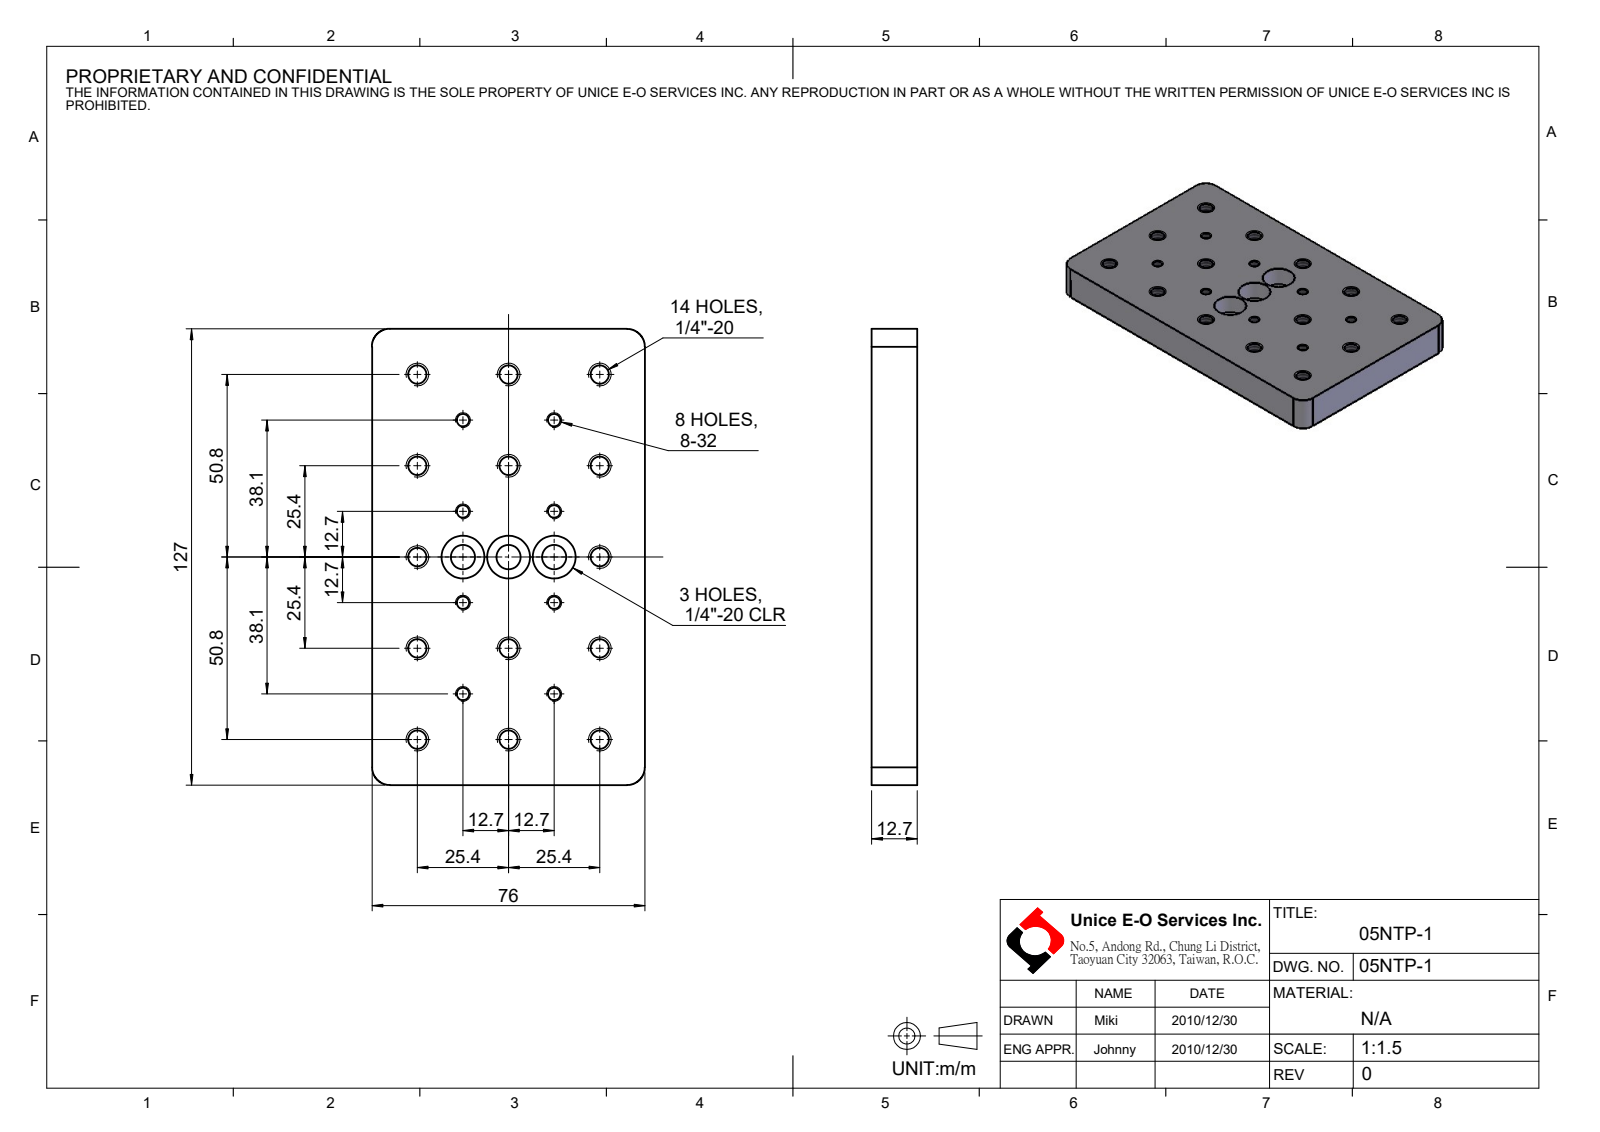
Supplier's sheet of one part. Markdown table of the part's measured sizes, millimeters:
| quantity | value |
| --- | --- |
| part name | 05NTP-1 |
| STEP written by | SolidWorks 2016 (CONFIG_CONTROL_DESIGN) |
| units | millimeters |
| bodies | 1 solid, 69 faces (9 planar, 60 cylindrical, 0 other) |
| overall size | 127 × 76 × 12.7 |
| volume | 114 765 mm³ |
| surface area | 28 473 mm² |
| round holes (diameter × count) | 5.11 × 14, 3.45 × 8, 6.76 × 3, 11.91 × 3 |
| partial cylindrical surfaces (radius × count) | 5 × 4 |
| main face-to-face distances | 12.7, 76, 127, 5.7, 7 |
| hole center spacings | 40.16, 25.4, 17.96, 56.8, 35.92, 50.8, 64.76, 28.4 |
